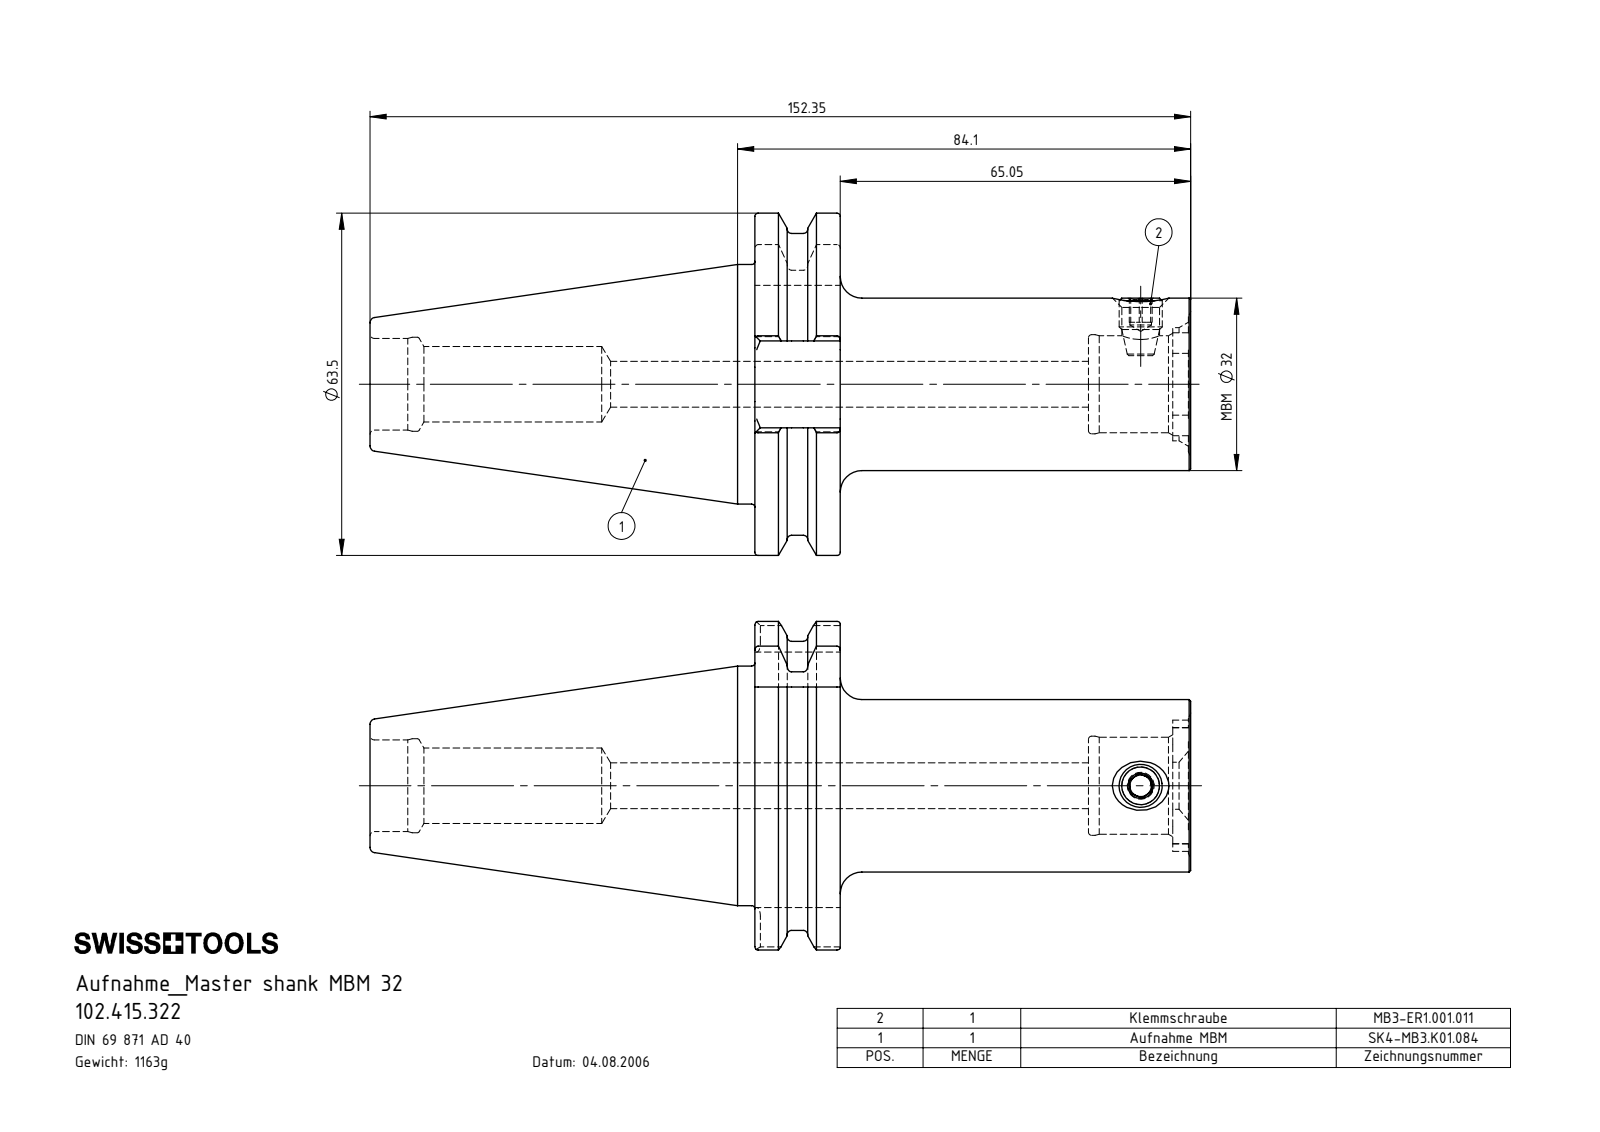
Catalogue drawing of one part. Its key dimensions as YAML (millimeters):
part_name: "SK4-MB3.K01.084_C; 102.415.322; MB3-ER1.001.011_A"
step_written_by: "SolidWorks 2017 (CONFIG_CONTROL_DESIGN)"
units: millimeters
bodies: {solids: 2, faces: 171, planar: 55, cylindrical: 50, other: 66}
overall_size: [152.35, 63.5, 60.94]
volume: 148159
surface_area: 28601
round_holes:
  - {diameter: 4, count: 1}
  - {diameter: 7, count: 1}
  - {diameter: 8.5, count: 1}
  - {diameter: 14, count: 1}
  - {diameter: 17, count: 1}
  - {diameter: 17.45, count: 1}
  - {diameter: 18, count: 1}
  - {diameter: 18.4, count: 1}
round_bosses_or_shafts:
  - {diameter: 44.45, count: 1}
  - {diameter: 32, count: 1}
  - {diameter: 8, count: 1}
partial_cylinders:
  - {radius: 1.6, count: 8}
  - {radius: 3.2, count: 4}
  - {radius: 10.5, count: 1}
  - {radius: 12.18, count: 1}
  - {radius: 28, count: 1}
  - {radius: 31.75, count: 1}
face_to_face_distances: [15.85, 47.4, 80.9, 65.05, 61.9, 46.05, 19, 77.55, 61.7, 15.65]
